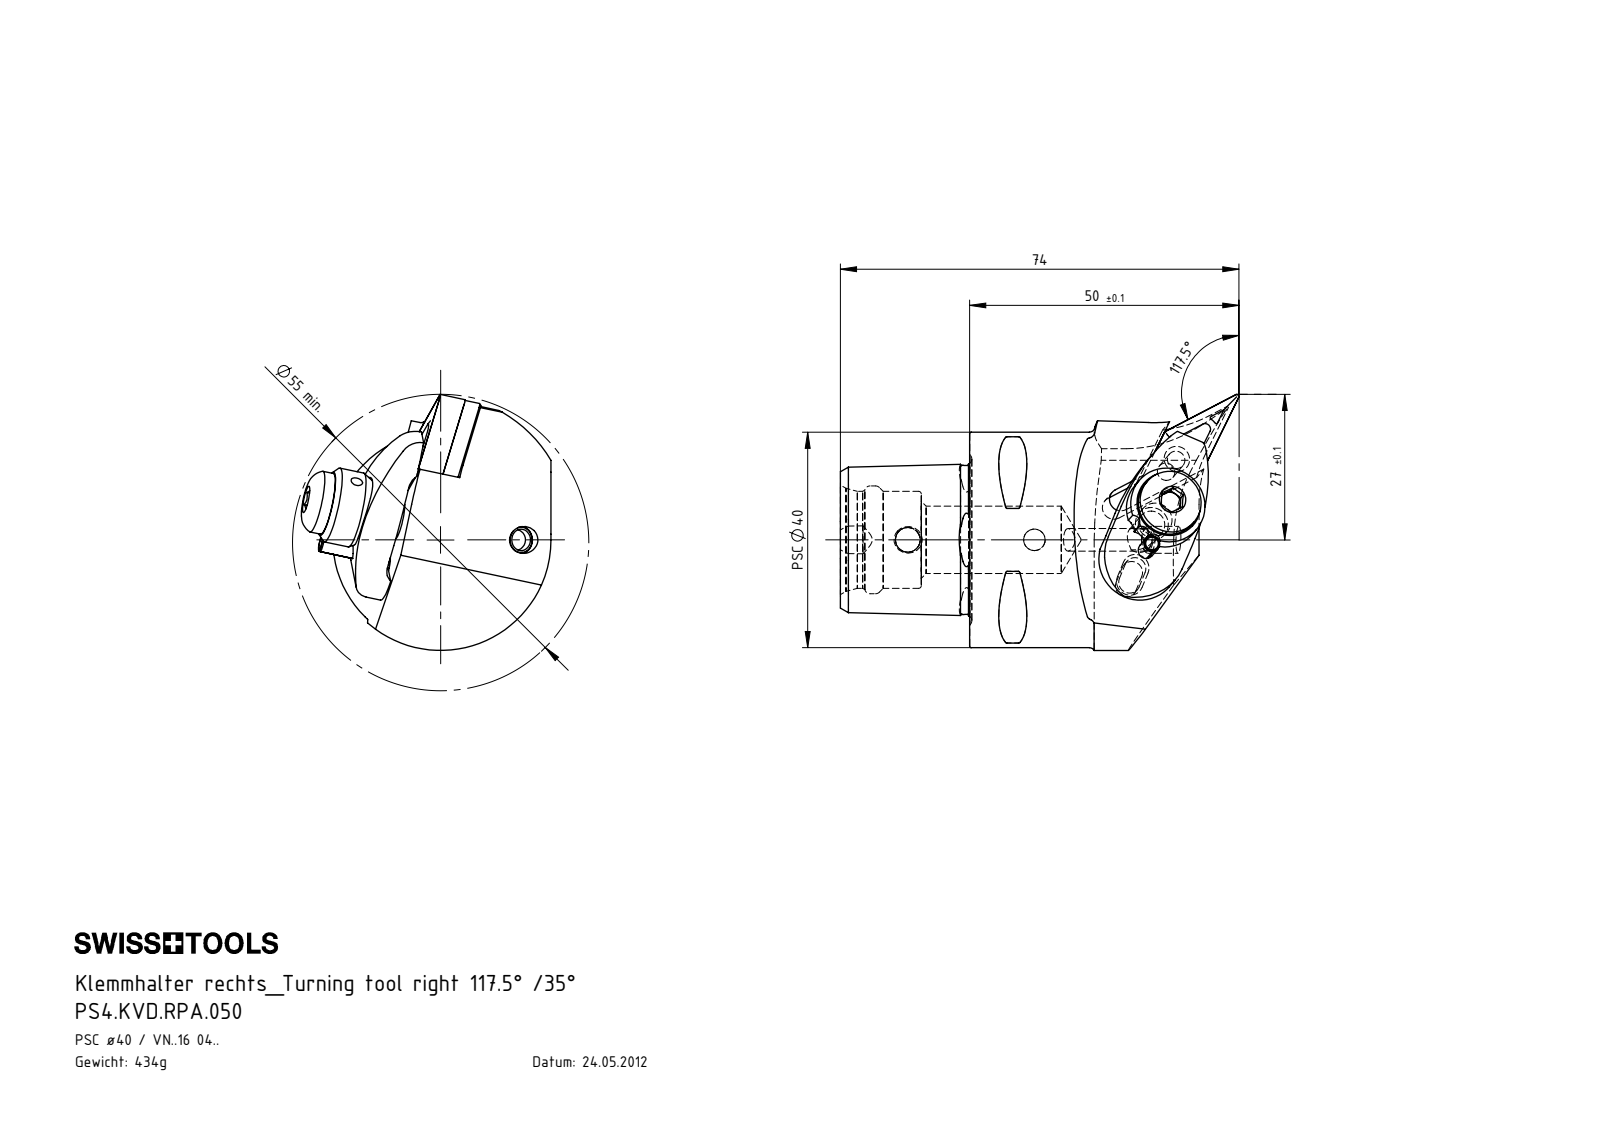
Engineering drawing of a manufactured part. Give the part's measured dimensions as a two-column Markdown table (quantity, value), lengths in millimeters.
| quantity | value |
| --- | --- |
| part name | WCC-ER3.102.024_C; ISO 13337 - 3 x 12_PreviewCfg; PS4-KVD.RPA.050_A; KVT_MB_600_050 (+7 more) |
| STEP written by | SolidWorks 2017 (AUTOMOTIVE_DESIGN) |
| units | millimeters |
| bodies | 11 solids, 445 faces (100 planar, 134 cylindrical, 211 other) |
| overall size | 74 × 47.5 × 46.34 |
| volume | 54 704 mm³ |
| surface area | 17 780 mm² |
| round holes (diameter × count) | 2 × 3, 4 × 2, 7 × 2, 2.4 × 1, 3 × 1, 3.3 × 1, 3.8 × 1, 4.2 × 1, 4.6 × 1, 4.95 × 1, 5 × 1, 6.2 × 1 |
| round bosses / shafts (diameter × count) | 4 × 2, 3 × 2, 40 × 1, 14 × 1, 11.5 × 1, 6.8 × 1, 6.2 × 1, 6 × 1 |
| partial cylindrical surfaces (radius × count) | 0.3 × 8, 0.34 × 6, 0.59 × 6, 0.4 × 4, 1.5 × 3, 3 × 3, 0.5 × 2, 2 × 2 |
| main face-to-face distances | 7.63, 3.18, 4.45, 8.93, 5.75, 1.3, 24, 9.52, 15.52, 9.08 |
| hole center spacings | 8.02, 14.3, 22.32, 8.01, 8.03, 8.19, 8.2, 14.12 |
